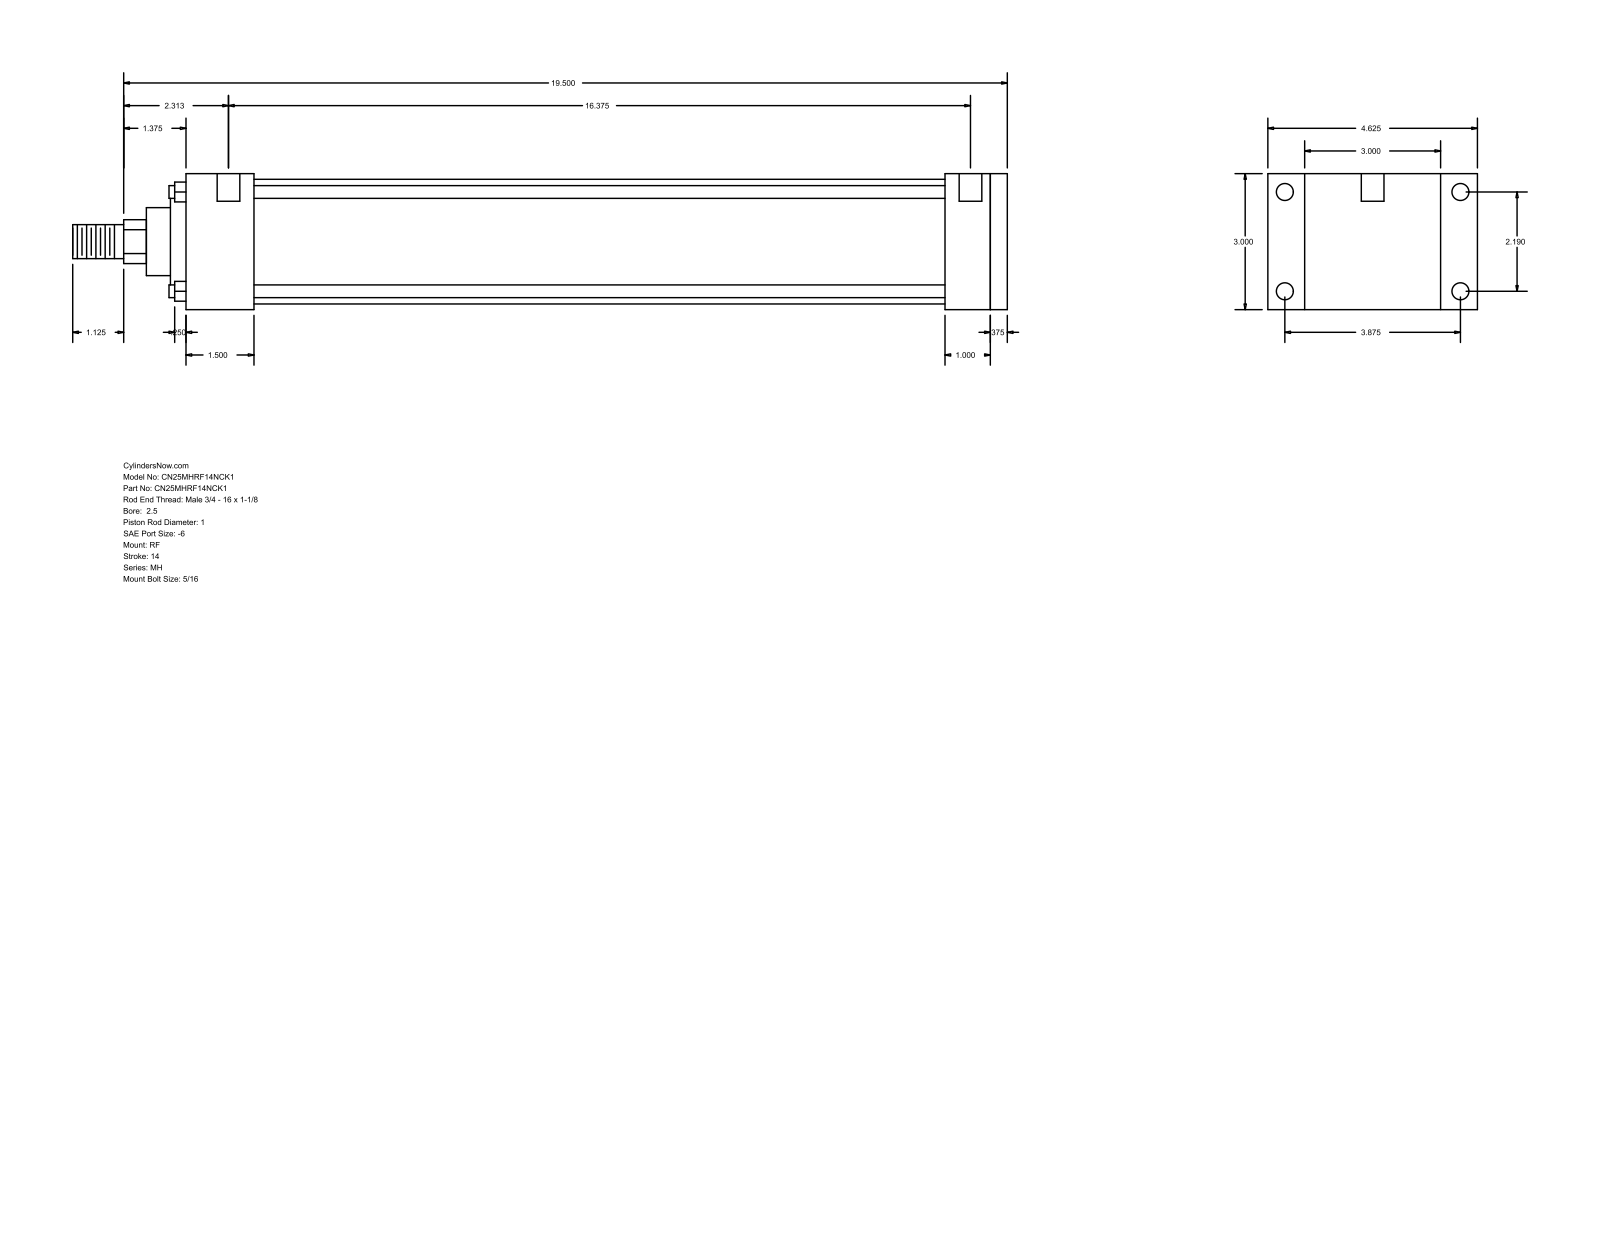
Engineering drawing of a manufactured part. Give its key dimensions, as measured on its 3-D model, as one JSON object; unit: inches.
{"part_name": "MH_RF__0250_1", "step_written_by": "GSSL Pune (CONFIG_CONTROL_DESIGN)", "units": "inches", "bodies": {"solids": 0, "faces": 94, "planar": 65, "cylindrical": 29, "other": 0}, "overall_size": [20.625, 4.625, 3], "round_holes": [[0.219, 4], [0.375, 4], [0.5, 2]], "round_bosses_or_shafts": [[0.281, 4], [2.75, 1], [2.375, 1], [1.5, 1], [1, 1], [0.75, 1]], "partial_cylinders_radius": [[0.484, 1]], "face_to_face_distances": [3, 0.375, 18.125, 17.75, 1.375, 1, 16.75, 1.5, 15.25, 16.25], "hole_center_spacings": [2.19, 3.875, 4.451, 16.687, 0.125, 0.187, 16.375, 16.5]}
